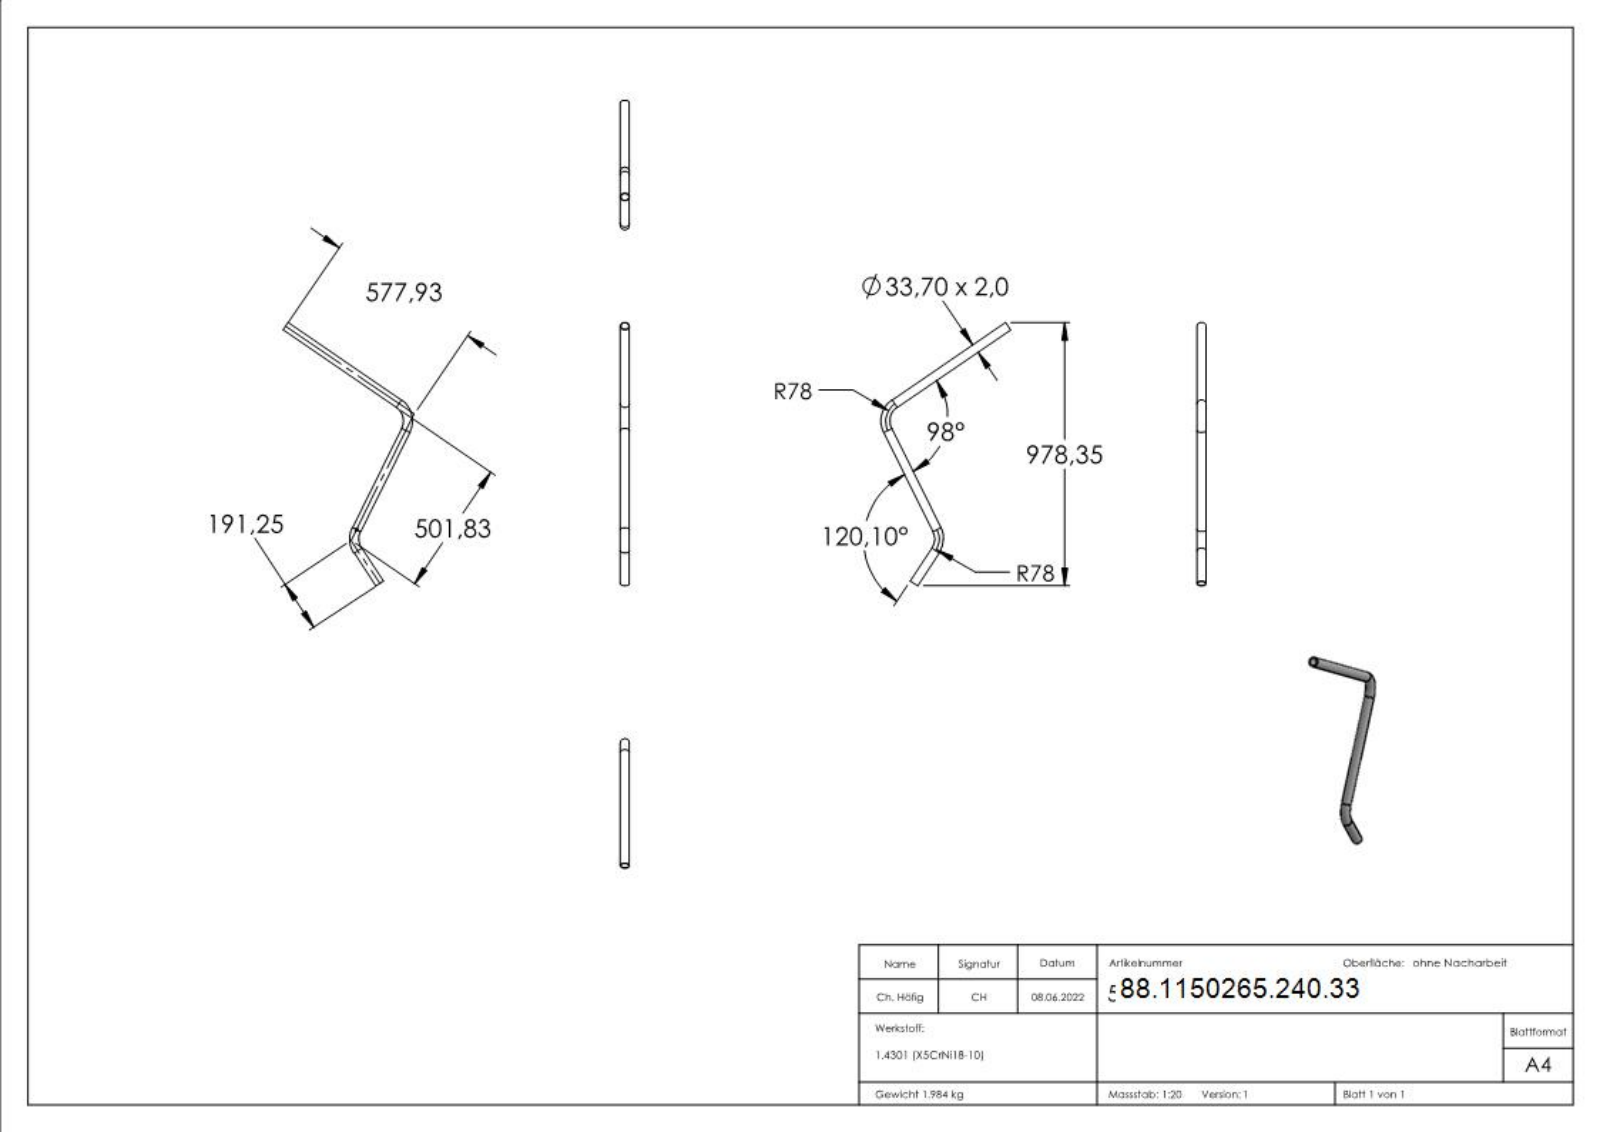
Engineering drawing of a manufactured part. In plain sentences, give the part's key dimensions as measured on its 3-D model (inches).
The part is named "50265-240-33". Its 3-D file was written by "SolidWorks 2018 (CONFIG_CONTROL_DESIGN)". It is 1 solid with 323 faces: 110 planar, 34 cylindrical and 179 other. Overall it measures 38.518 by 18.946 by 1.327 inches. Its volume is 15.32 cubic inches and its surface area 389.8 square inches. Round holes: 3 of diameter 1.169. Round bosses or shafts: 3 of diameter 1.327. Partial cylindrical surfaces (rounded edges, fillets, slot ends): 1 of radius 0.589. The main face-to-face distances are 0.161, 0.117, 0.049, 0.112, 0.129, 0.08, 0.156, 0.142, 0.044, 0.107.
